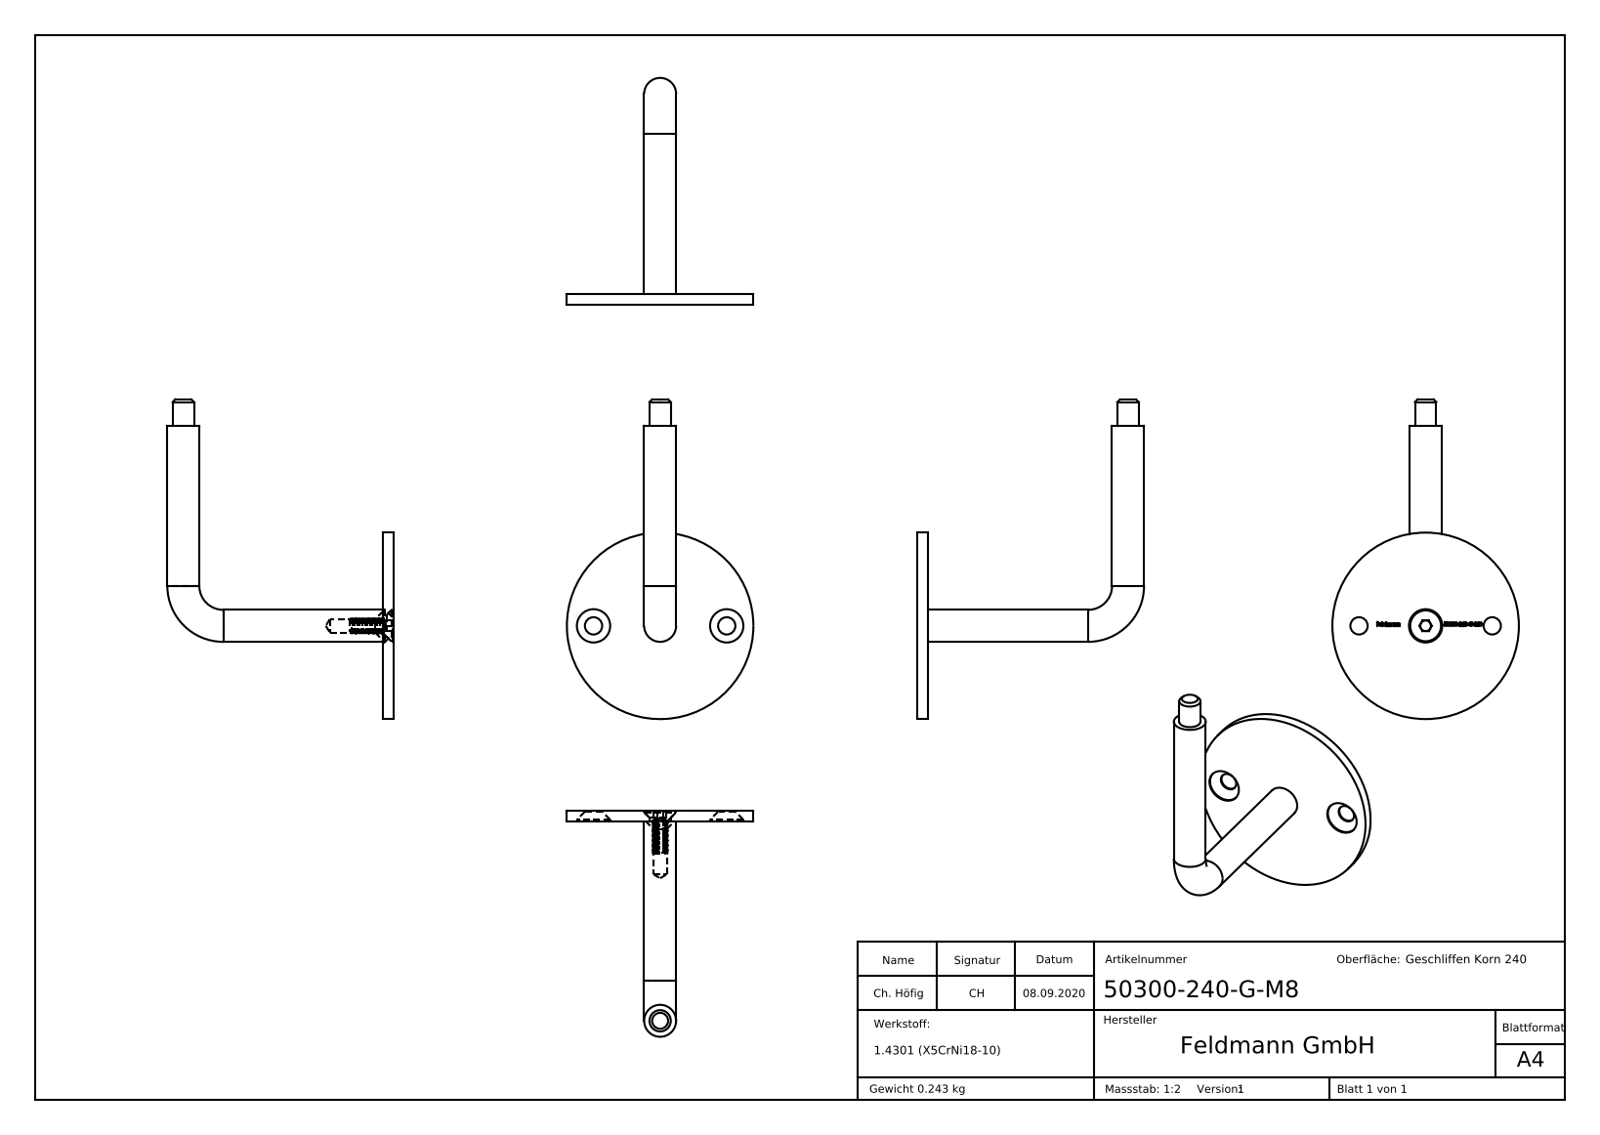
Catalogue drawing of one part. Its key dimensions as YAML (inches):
part_name: "socket countersunk head screw_din; 50300-240-G-M8 Teil2_50300-240-G-M8 Teil2; 50300-240-G-M8; 50300-240-G-M8 Teil2 (+3 more)"
step_written_by: "SolidWorks 2018 (CONFIG_CONTROL_DESIGN)"
units: inches
bodies: {solids: 3, faces: 418, planar: 162, cylindrical: 48, other: 208}
overall_size: [4.724, 3.346, 2.756]
volume: 1.905
surface_area: 23.84
round_holes:
  - {diameter: 0.492, count: 3}
  - {diameter: 0.256, count: 2}
  - {diameter: 0.197, count: 1}
  - {diameter: 0.315, count: 1}
round_bosses_or_shafts:
  - {diameter: 0.472, count: 2}
  - {diameter: 2.756, count: 1}
  - {diameter: 0.456, count: 1}
  - {diameter: 0.315, count: 1}
  - {diameter: 0.236, count: 1}
face_to_face_distances: [0.157, 0.14, 0.018, 0.394, 0.648, 0.63, 0.49, 0.158, 0.014, 0.154]
hole_center_spacings: [0.984, 1.969]
